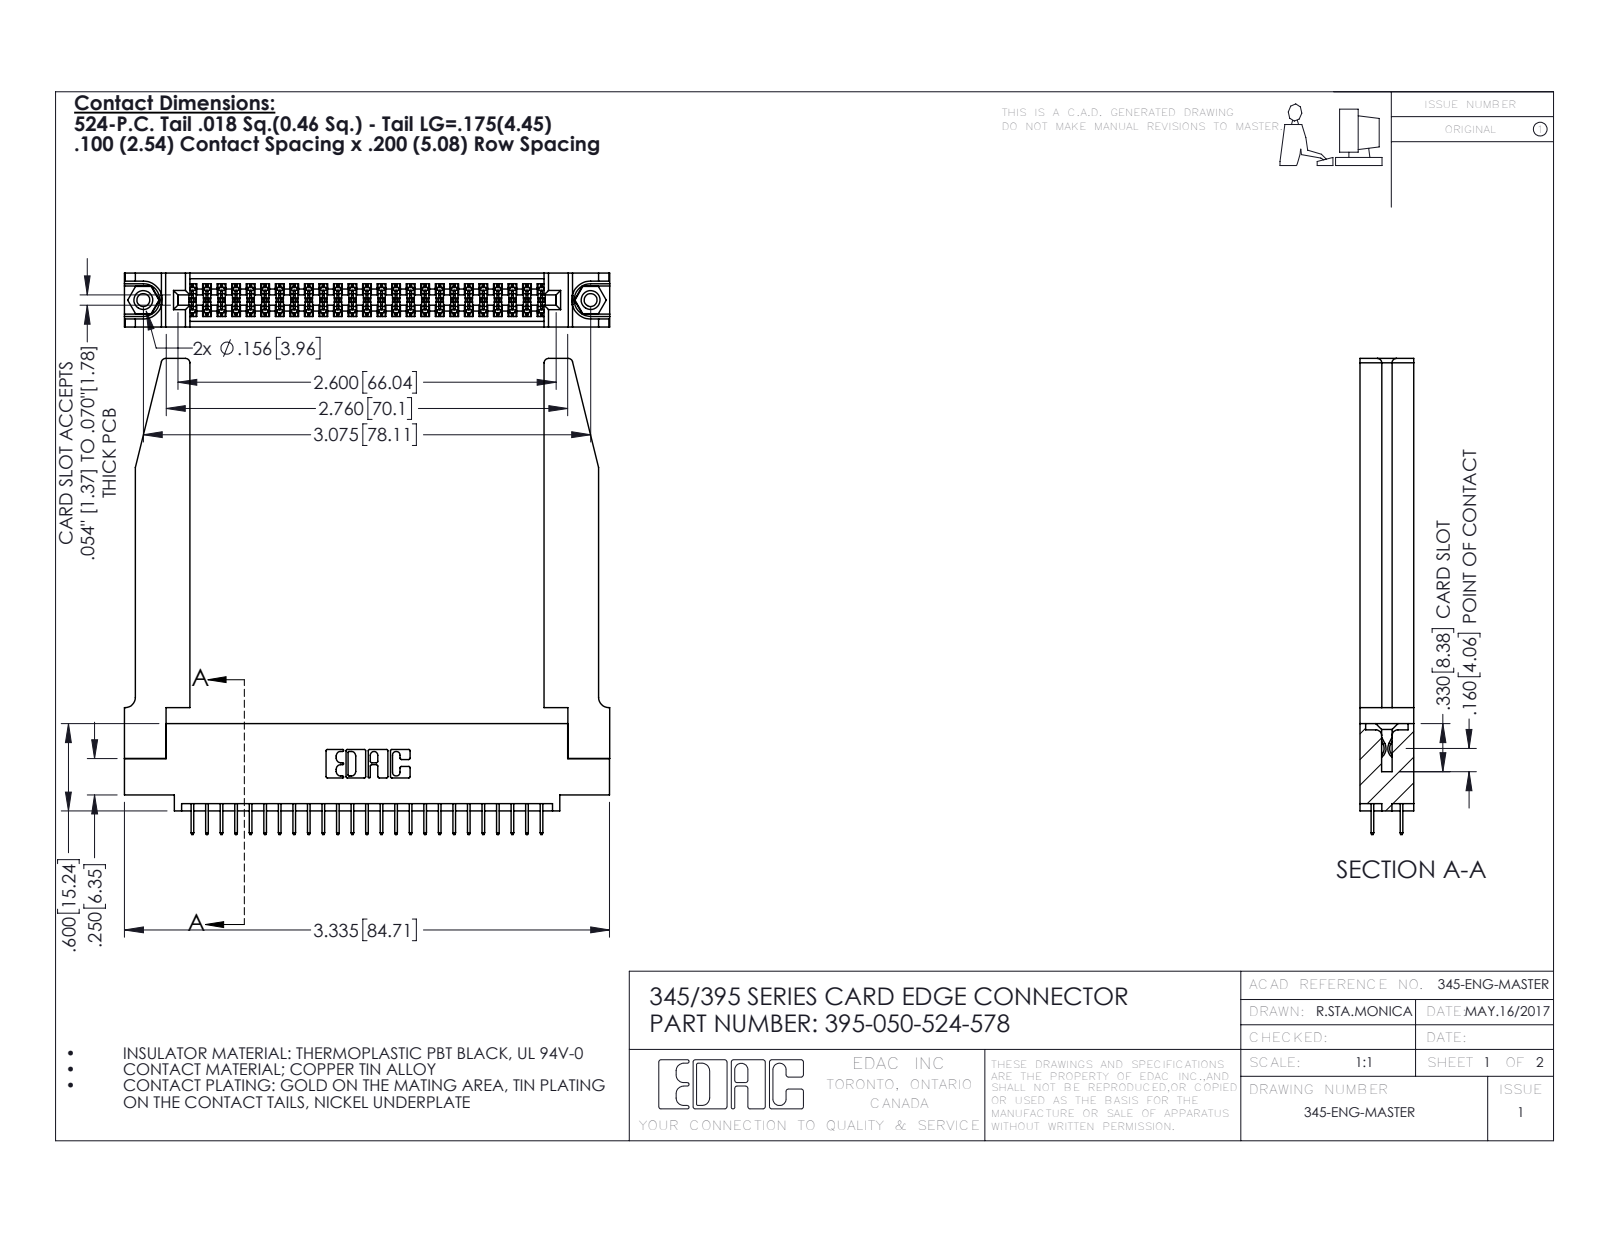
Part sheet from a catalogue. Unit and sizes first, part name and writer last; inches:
Units: inches
Overall size (bounding box): 3.336 × 3.272 × 0.37
Round holes (diameter × count): ⌀0.089 ×2, ⌀0.125 ×2, ⌀0.156 ×2, ⌀0.064 ×1
Round bosses / shafts (diameter × count): ⌀0.155 ×2
Partial cylindrical surfaces — rounded edges, fillets, slot ends (radius × count): R0.006 ×75, R0.01 ×22, R0.03 ×8, R0.007 ×6, R0.031 ×6, R0.026 ×3, R0.014 ×2, R0.019 ×2
Main face-to-face distances: 0.37, 0.072, 0.298, 0.2, 0.098, 0.272, 0.025, 0.225, 0.148, 0.15
Hole centre spacings: 0.27, 2.84, 3.075
Volume: 0.958 in³ · Surface area: 28.08 in²
Bodies: 55 solids, 3064 faces (2176 planar, 836 cylindrical, 52 other)
Part name (STEP PRODUCT): 345-220-078_345-220-078; 395-050-524-578; 345-292-001_345-293-124; 345-250-001_345-250-001-102 (+1 more)
STEP written by: SolidWorks 2016 (CONFIG_CONTROL_DESIGN)
